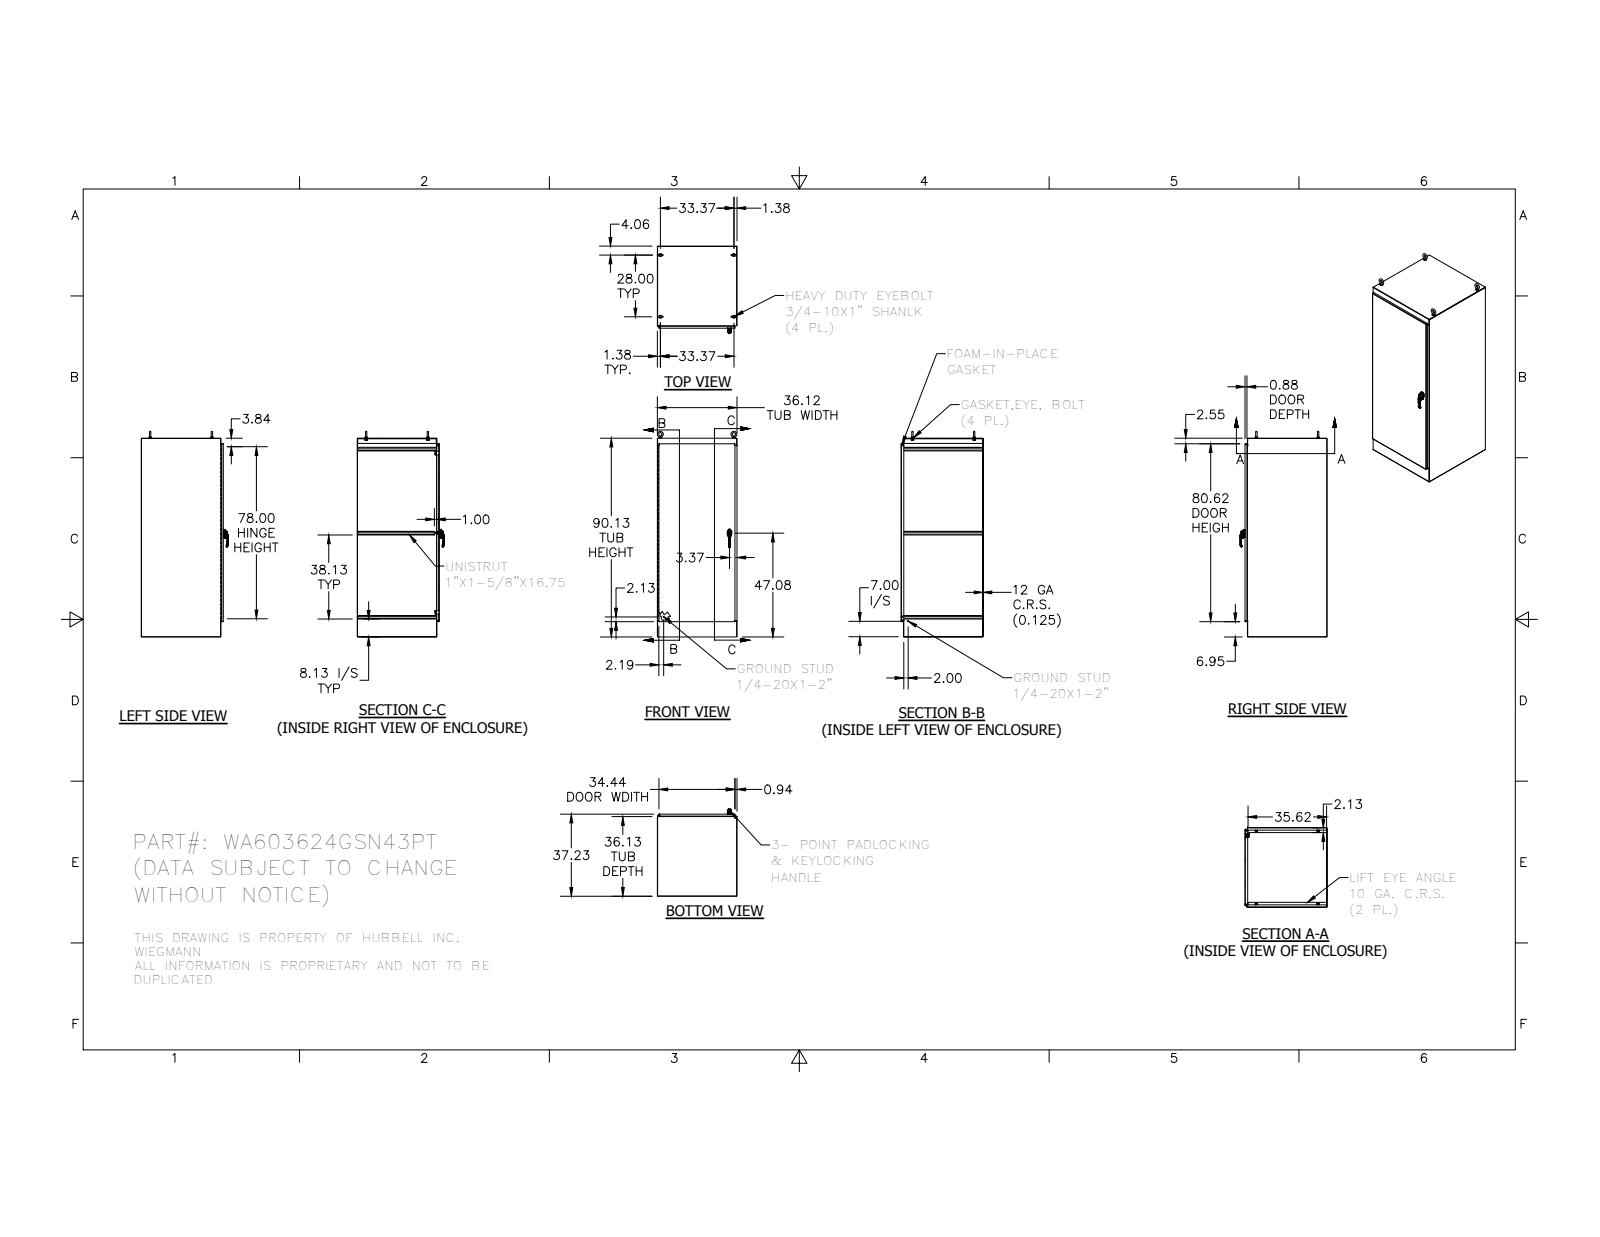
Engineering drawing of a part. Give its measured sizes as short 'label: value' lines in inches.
name: 1091-903_AF0_2; 349132; 31215; 1091-903_AF0_1 (+8 more)
written by: SolidWorks 2014 (AUTOMOTIVE_DESIGN)
unit: in
bodies: 58 solids, 2140 faces (857 planar, 755 cylindrical, 528 other)
size: 93.248 × 37.23 × 36.125
volume: 2 221 in³; area: 35 889 in²
holes: 8× ⌀0.277, 8× ⌀0.375, 4× ⌀0.2, 4× ⌀0.642, 4× ⌀0.813, 3× ⌀0.28, 2× ⌀0.241, 2× ⌀0.25, 2× ⌀0.252, 2× ⌀0.4, 2× ⌀0.407, 2× ⌀0.45
bosses: 4× ⌀1.25, 4× ⌀1.12, 4× ⌀0.75, 2× ⌀1, 2× ⌀0.563, 2× ⌀0.527, 2× ⌀0.5, 2× ⌀0.375
rounds: 16× R0.01, 16× R0.125, 15× R0.031, 15× R0.156, 14× R0.05, 12× R0.019, 12× R0.053, 12× R0.086
face distances: 0.125, 36, 35.875, 36.125, 0.125, 36.98, 37.105, 37.23, 37.104, 90
hole spacings: 8.667, 26, 17.333, 34.667, 71.883, 72.633, 0.762, 0.764
